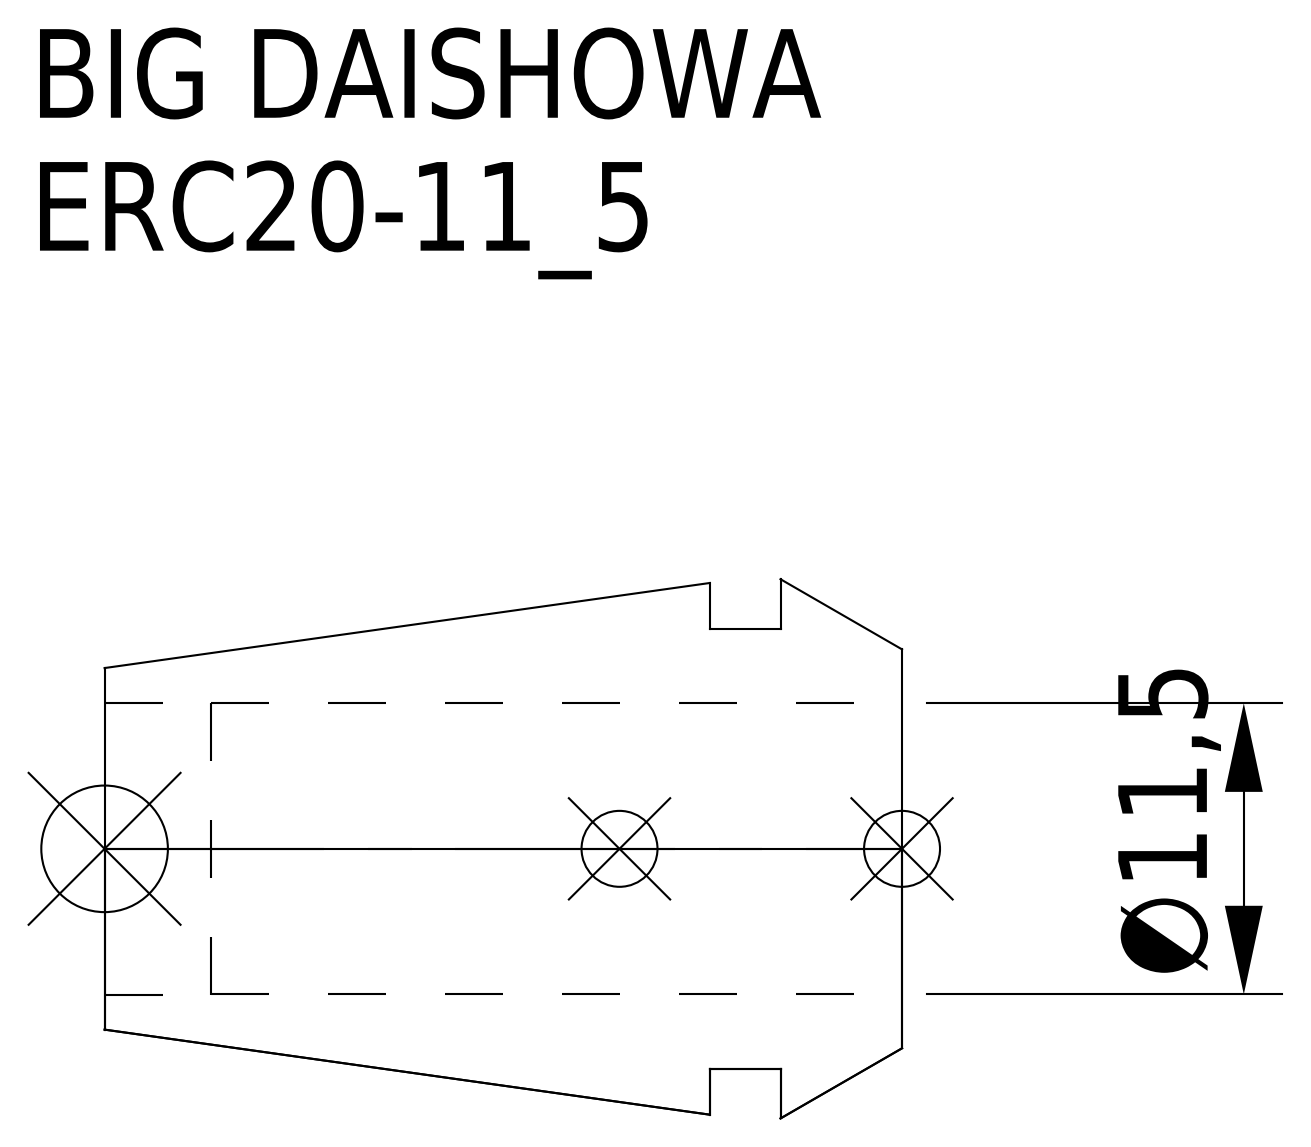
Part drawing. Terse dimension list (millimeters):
name: ERC20-11_5
written by: CREO PARAMETRIC BY PTC INC, 2016380 (AUTOMOTIVE_DESIGN)
unit: mm
bodies: 1 solid, 15 faces (5 planar, 6 cylindrical, 4 other)
size: 31.5 × 21.3 × 21.3
volume: 4 607 mm³; area: 3 327 mm²
holes: 1× ⌀11.5, 1× ⌀11.55
bosses: 1× ⌀17.4
face distances: 2.8, 4.8, 7.6, 31.5, 26.7, 23.9, 27.3, 22.5, 19.7, 4.2
